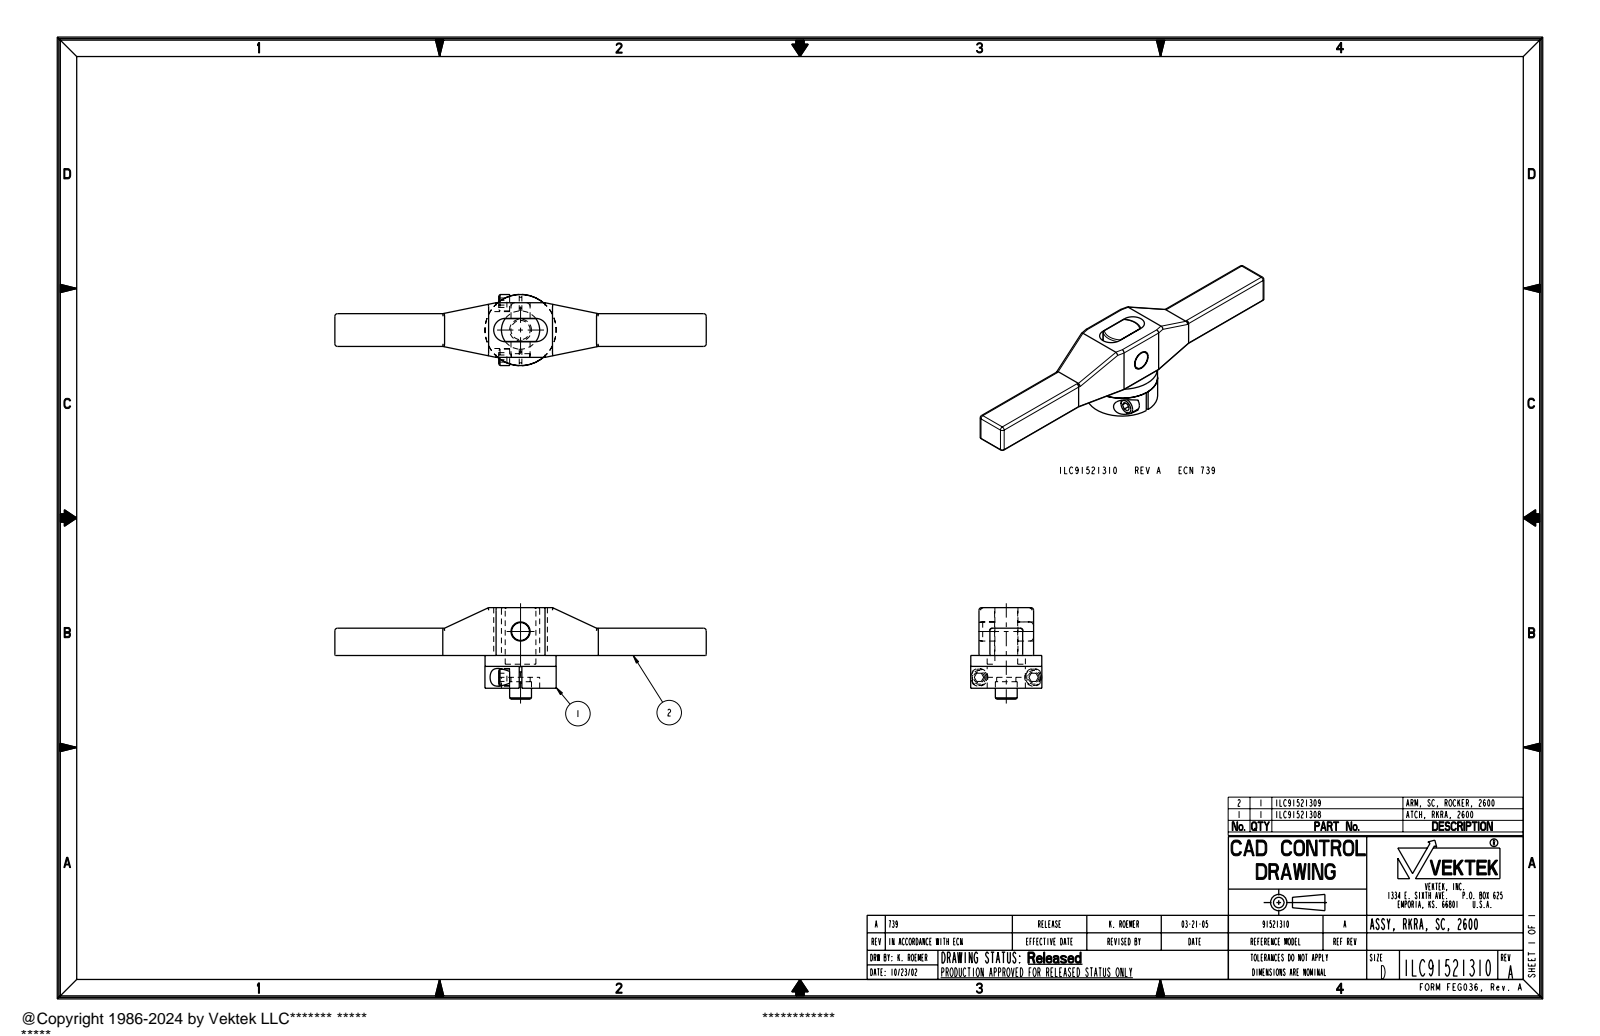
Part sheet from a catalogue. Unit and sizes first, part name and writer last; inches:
Units: inches
Overall size (bounding box): 8.5 × 2.094 × 1.629
Round holes (diameter × count): ⌀0.437 ×1, ⌀0.875 ×1
Round bosses / shafts (diameter × count): ⌀0.375 ×2, ⌀0.25 ×2, ⌀1.63 ×1, ⌀1.625 ×1, ⌀0.5 ×1, ⌀0.44 ×1, ⌀0.438 ×1
Partial cylindrical surfaces — rounded edges, fillets, slot ends (radius × count): R0.06 ×22, R0.02 ×10, R0.203 ×2, R0.267 ×2
Main face-to-face distances: 0.625, 0.75, 1, 0.25, 0.47, 0.364, 0.886, 0.114, 0.636, 0.75
Volume: 7.292 in³ · Surface area: 46.77 in²
Bodies: 2 solids, 153 faces (61 planar, 72 cylindrical, 20 other)
Part name (STEP PRODUCT): ILC91521308; ILC91521309; ILC91521310_ASM
STEP written by: PRO/ENGINEER BY PARAMETRIC TECHNOLOGY CORPORATION, 2004290 (AUTOMOTIVE_DESIGN_CC2)
